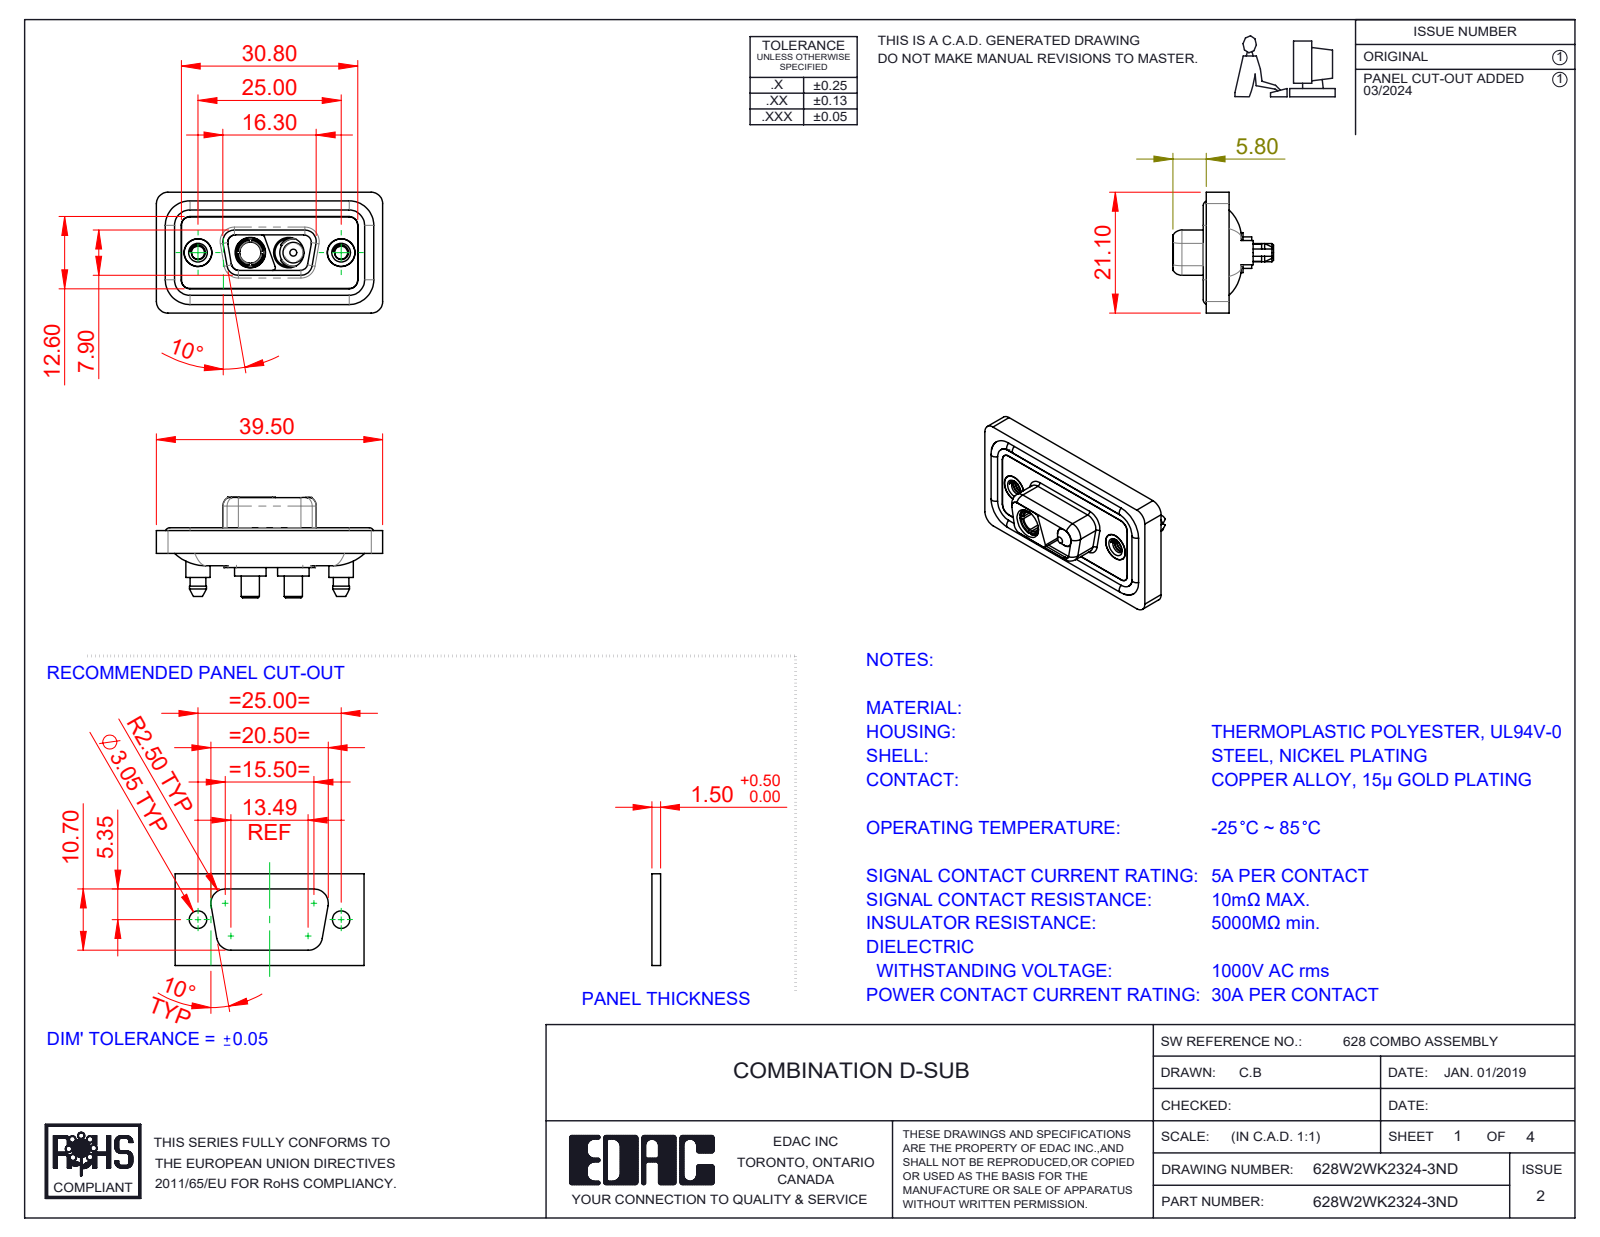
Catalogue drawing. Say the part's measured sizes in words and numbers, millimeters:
The part is named "628Combo Housing_2WK2; 628Combo Threaded Boardlock_D; 628W2WK2324-3ND; Power Socket_30A S (+4 more)". Its 3-D file was written by "SolidWorks 2023 (CONFIG_CONTROL_DESIGN)". It is 11 solids with 566 faces: 160 planar, 279 cylindrical and 127 other. Overall it measures 39.5 by 21.1 by 17.55 millimeters. Its volume is 4 753 cubic millimeters and its surface area 7 692 square millimeters. Round holes: 4 of diameter 4.85, 2 of diameter 2.26, 2 of diameter 4, 2 of diameter 4.05, 2 of diameter 5, 2 of diameter 5.3, 1 of diameter 3.7. Round bosses or shafts: 4 of diameter 1.6, 2 of diameter 5.5, 2 of diameter 5.4, 2 of diameter 5.2, 2 of diameter 4.95, 2 of diameter 4.8, 2 of diameter 4.75, 2 of diameter 4.25. Partial cylindrical surfaces (rounded edges, fillets, slot ends): 24 of radius 1.5, 18 of radius 2, 10 of radius 1.6, 8 of radius 1.35, 6 of radius 0.5, 4 of radius 0.25, 4 of radius 0.6, 4 of radius 0.65. The main face-to-face distances are 0.4, 1.1, 2.9, 1.6, 0.5, 1.8, 5.65, 1.5, 4, 5.35. The hole center spacings are 9.14, 15.86, 6.72, 25.
